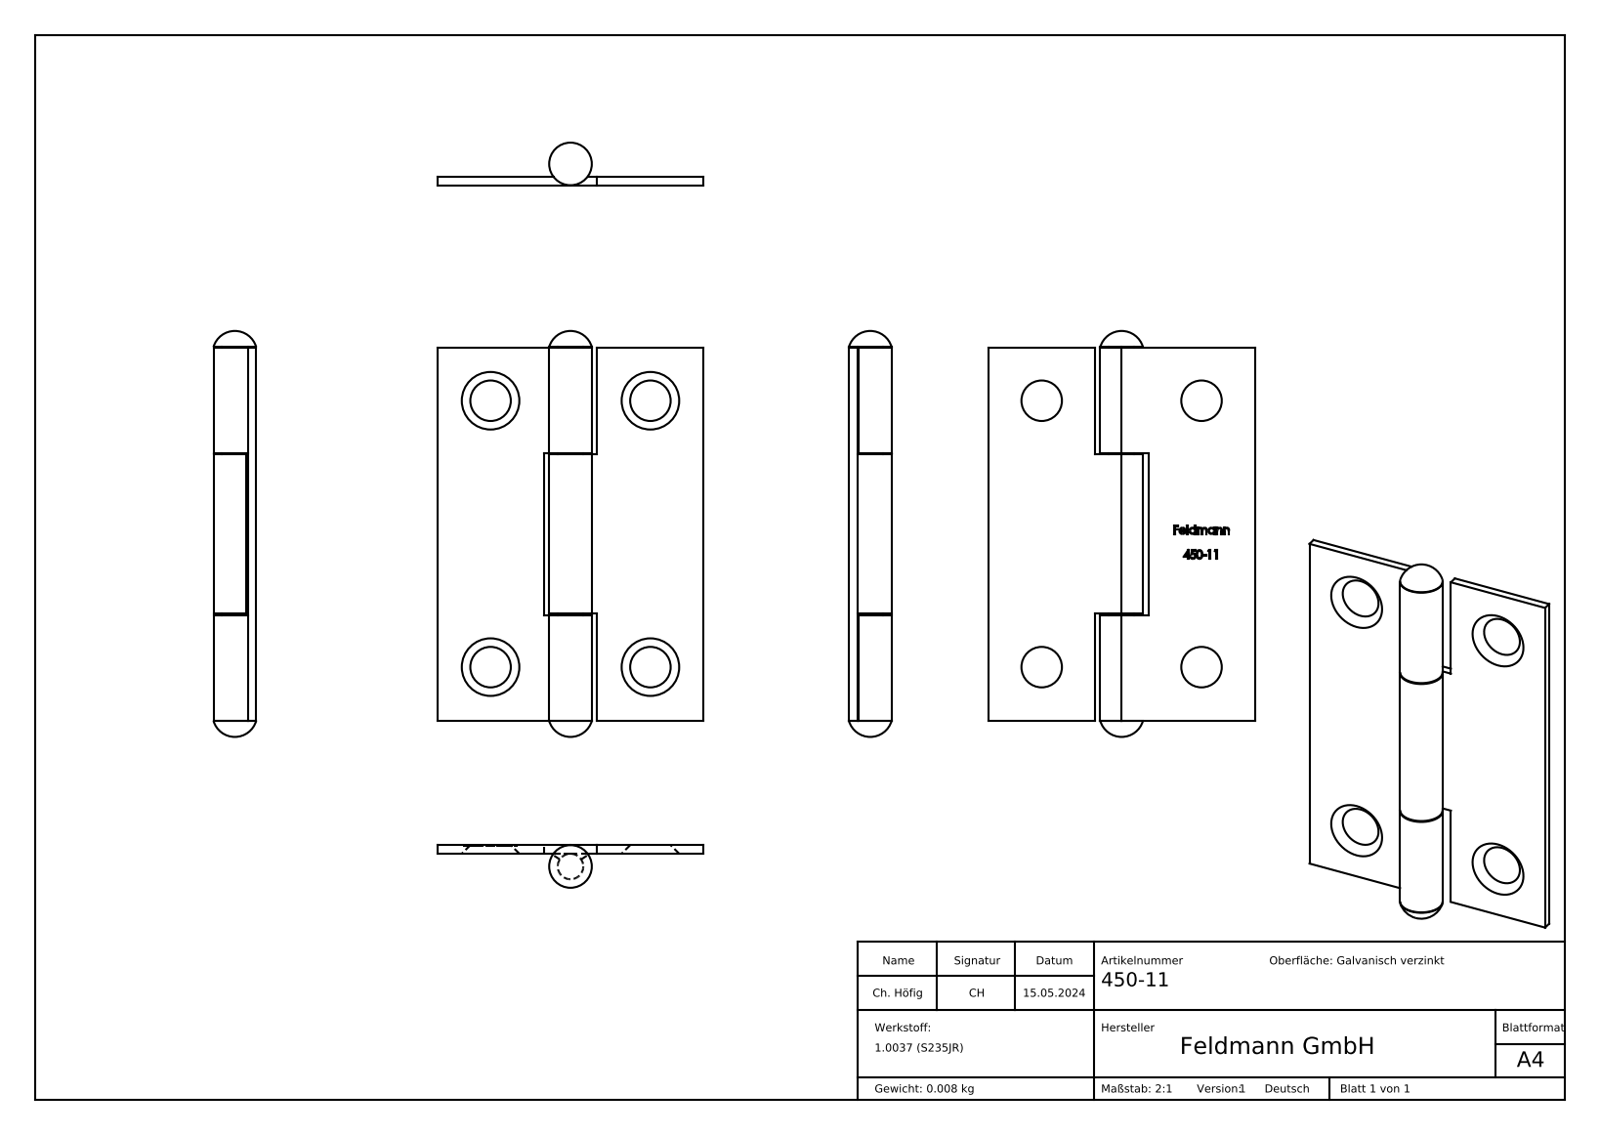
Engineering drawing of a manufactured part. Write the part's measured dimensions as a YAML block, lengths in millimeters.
part_name: "450-11 Teil2_450-11 Teil2; 450-11; 450-11 Teil3_450-11 Teil3; 450-11 Teil1_450-11 Teil1"
step_written_by: "SolidWorks 2018 (CONFIG_CONTROL_DESIGN)"
units: millimeters
bodies: {solids: 3, faces: 208, planar: 130, cylindrical: 7, other: 71}
overall_size: [38.1, 25, 4]
volume: 993
surface_area: 2613
round_holes:
  - {diameter: 2.4, count: 1}
round_bosses_or_shafts:
  - {diameter: 4, count: 1}
face_to_face_distances: [0.8, 10, 25, 15, 35, 9.9, 25.1, 15.1, 9.95, 10.05]
